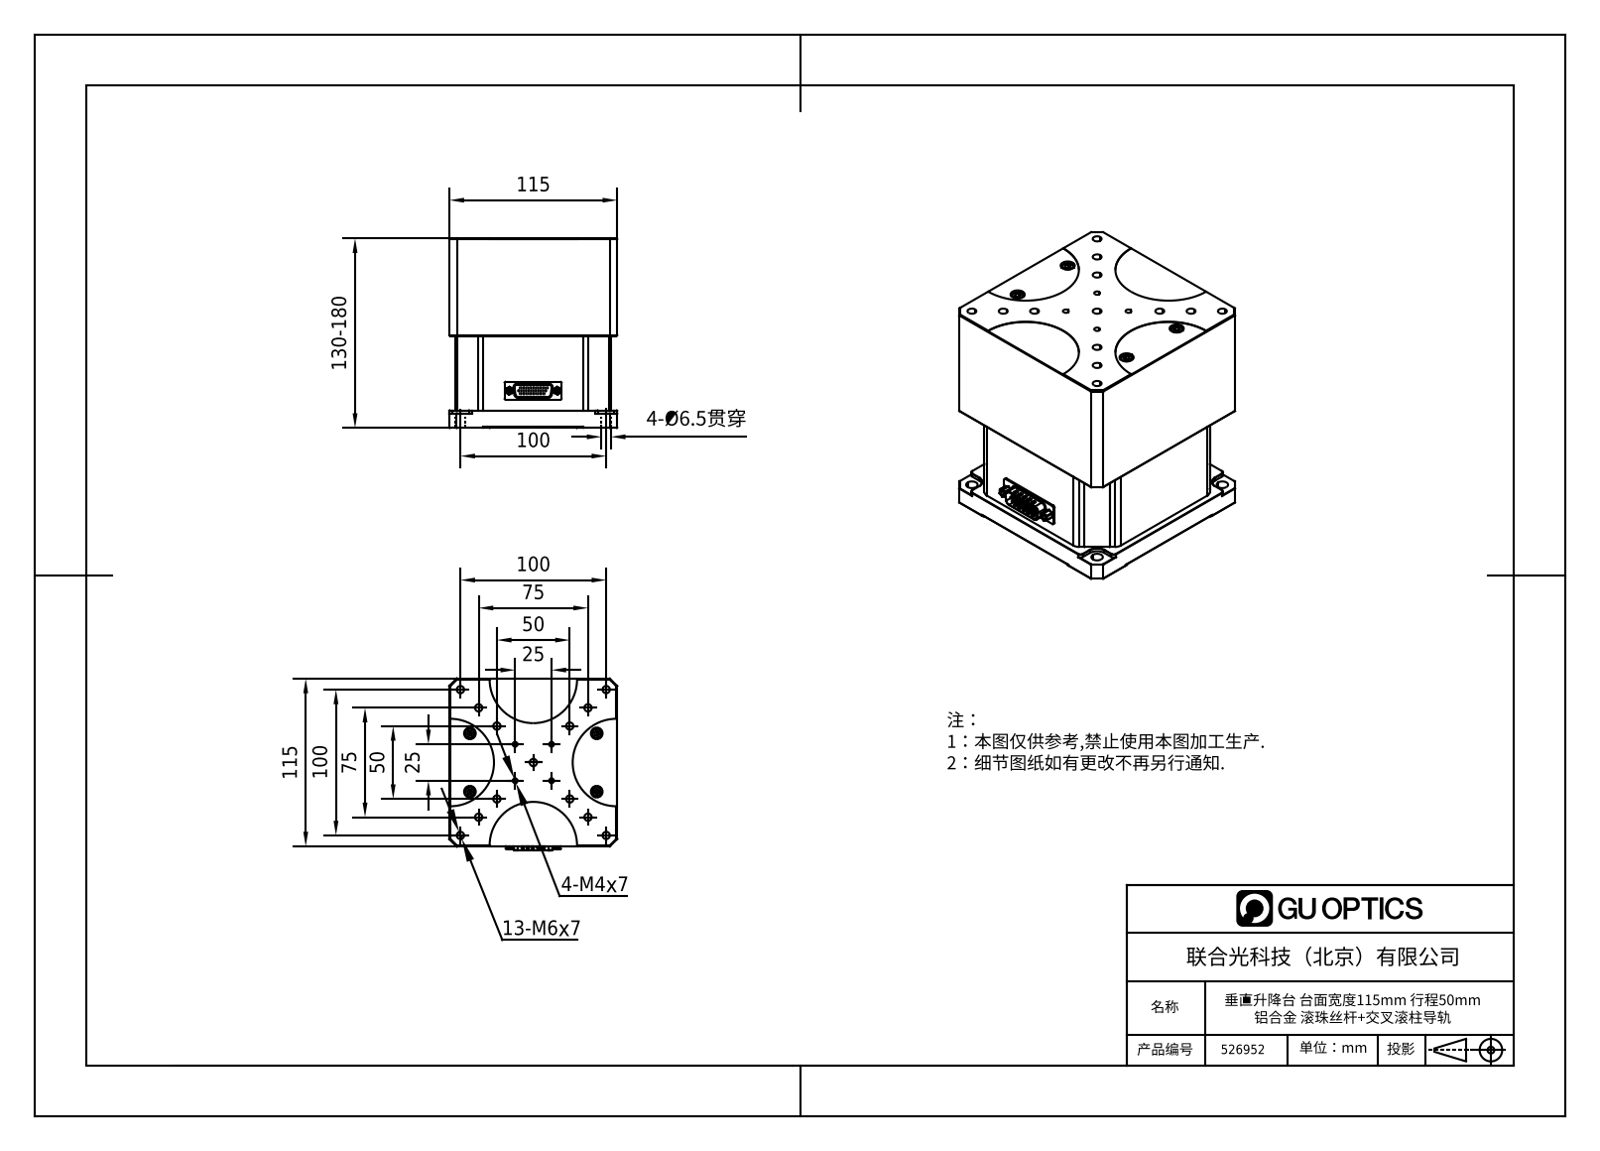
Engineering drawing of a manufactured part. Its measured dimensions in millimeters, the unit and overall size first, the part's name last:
Units: millimetres
Overall size (bounding box): 130 × 117.8 × 115.03
Round holes (diameter × count): ⌀5 ×13, ⌀1.5 ×8, ⌀2.2 ×8, ⌀3.3 ×4, ⌀4.3 ×4, ⌀6.5 ×4, ⌀8 ×4, ⌀2.5 ×2, ⌀3.2 ×1
Round bosses / shafts (diameter × count): ⌀1 ×26, ⌀2 ×8, ⌀7 ×4, ⌀4 ×4, ⌀3.8 ×2, ⌀3 ×1
Partial cylindrical surfaces — rounded edges, fillets, slot ends (radius × count): R0.5 ×36, R1 ×16, R5 ×16, R0.45 ×10, R0.4 ×8, R2 ×8, R2.2 ×8, R1.9 ×6
Main face-to-face distances: 115, 111, 4, 129.5, 107, 129.3, 3.97, 111.03, 110.97, 4.03
Hole centre spacings: 88.39, 17.68, 35.36, 53.03, 100, 70.71, 30.04, 39.53
Volume: 1 584 000 mm³ · Surface area: 93 569 mm²
Bodies: 1 solid, 1498 faces (555 planar, 554 cylindrical, 389 other)
Part name (STEP PRODUCT): 526952
STEP written by: SolidWorks 2020 (AUTOMOTIVE_DESIGN)
